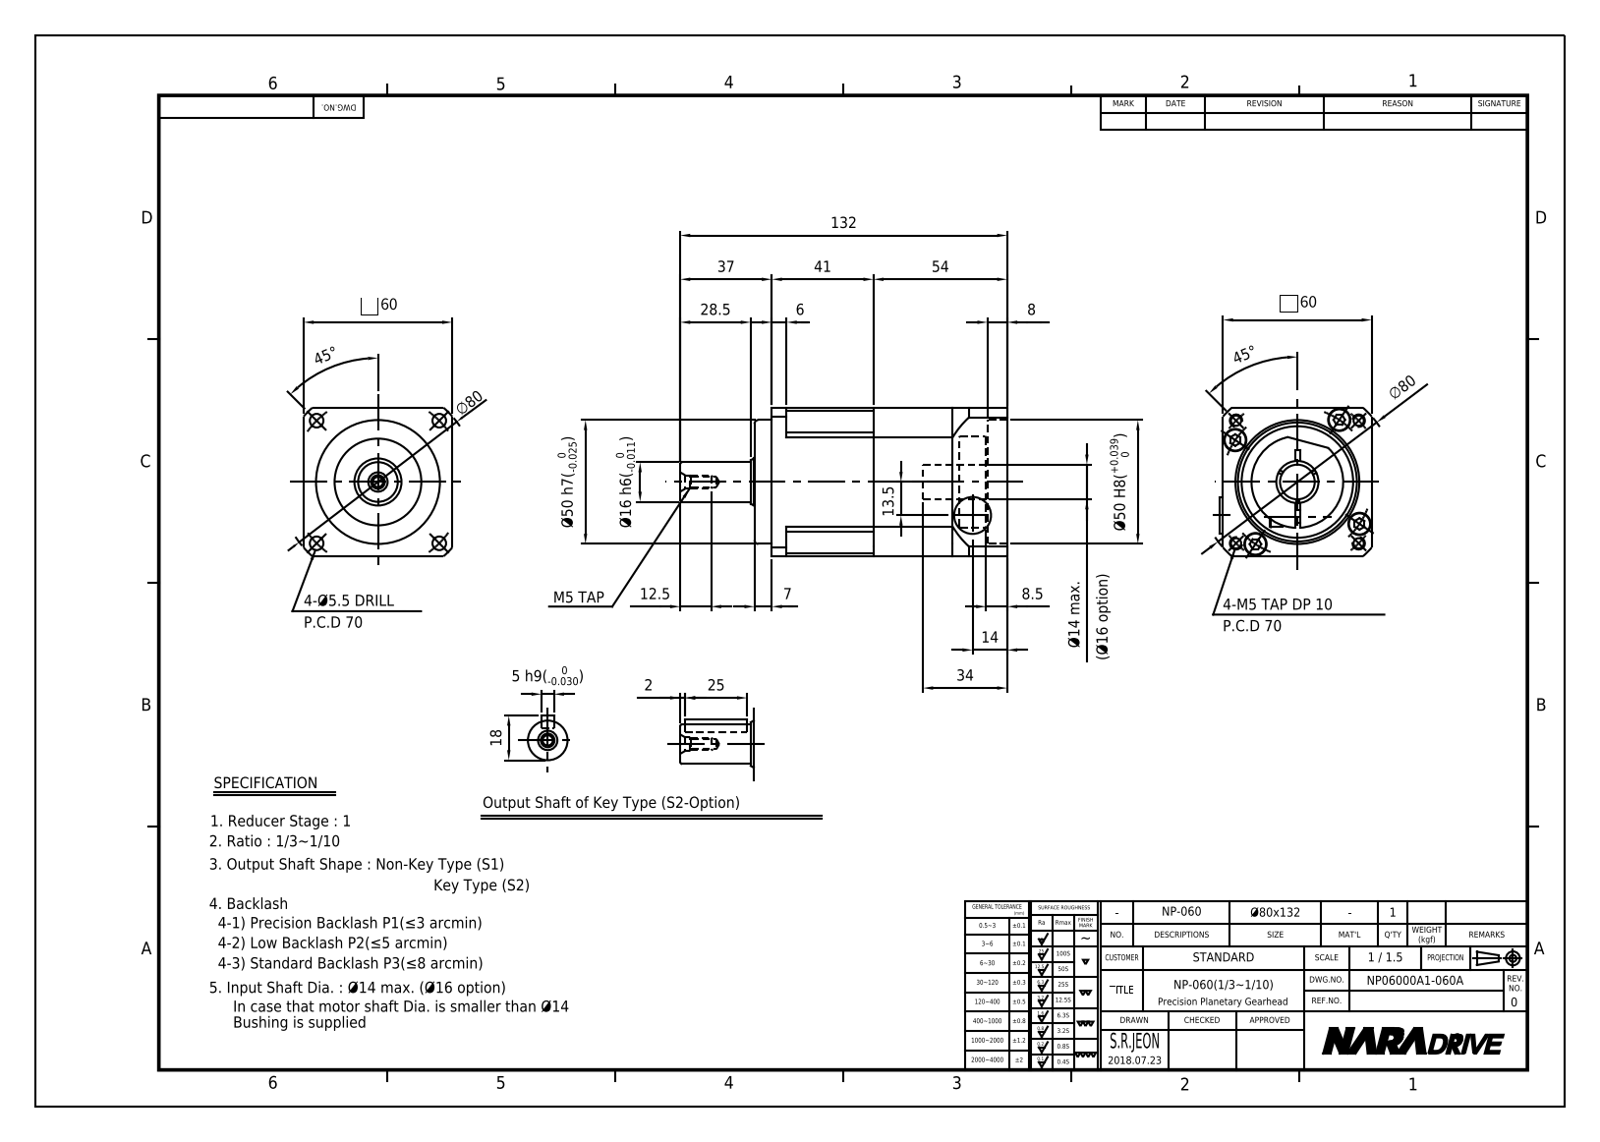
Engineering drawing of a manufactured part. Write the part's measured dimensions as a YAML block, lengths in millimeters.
part_name: "NP06000A1-060A-S1"
step_written_by: "Autodesk Inventor 2015 (AUTOMOTIVE_DESIGN)"
units: millimeters
bodies: {solids: 2, faces: 325, planar: 150, cylindrical: 94, other: 81}
overall_size: [132, 61.5, 60]
volume: 230604
surface_area: 55991
round_holes:
  - {diameter: 4.13, count: 9}
  - {diameter: 5.5, count: 9}
  - {diameter: 3.24, count: 4}
  - {diameter: 4.2, count: 4}
  - {diameter: 7.5, count: 4}
  - {diameter: 9, count: 4}
  - {diameter: 7, count: 1}
  - {diameter: 8.5, count: 1}
  - {diameter: 14, count: 1}
  - {diameter: 17, count: 1}
  - {diameter: 45, count: 1}
  - {diameter: 48, count: 1}
round_bosses_or_shafts:
  - {diameter: 8.5, count: 5}
  - {diameter: 5, count: 5}
  - {diameter: 37, count: 1}
  - {diameter: 35, count: 1}
  - {diameter: 19, count: 1}
  - {diameter: 16, count: 1}
  - {diameter: 15, count: 1}
  - {diameter: 8, count: 1}
partial_cylinders:
  - {radius: 0.5, count: 4}
  - {radius: 7, count: 4}
  - {radius: 2.07, count: 1}
  - {radius: 4.5, count: 1}
  - {radius: 35, count: 1}
  - {radius: 40, count: 1}
face_to_face_distances: [60, 46, 39, 7, 95, 102, 56, 19.5, 82.5, 75.5]
hole_center_spacings: [30.25, 42.78, 8.77, 35, 40.79, 49.5, 50.44, 50.74]
